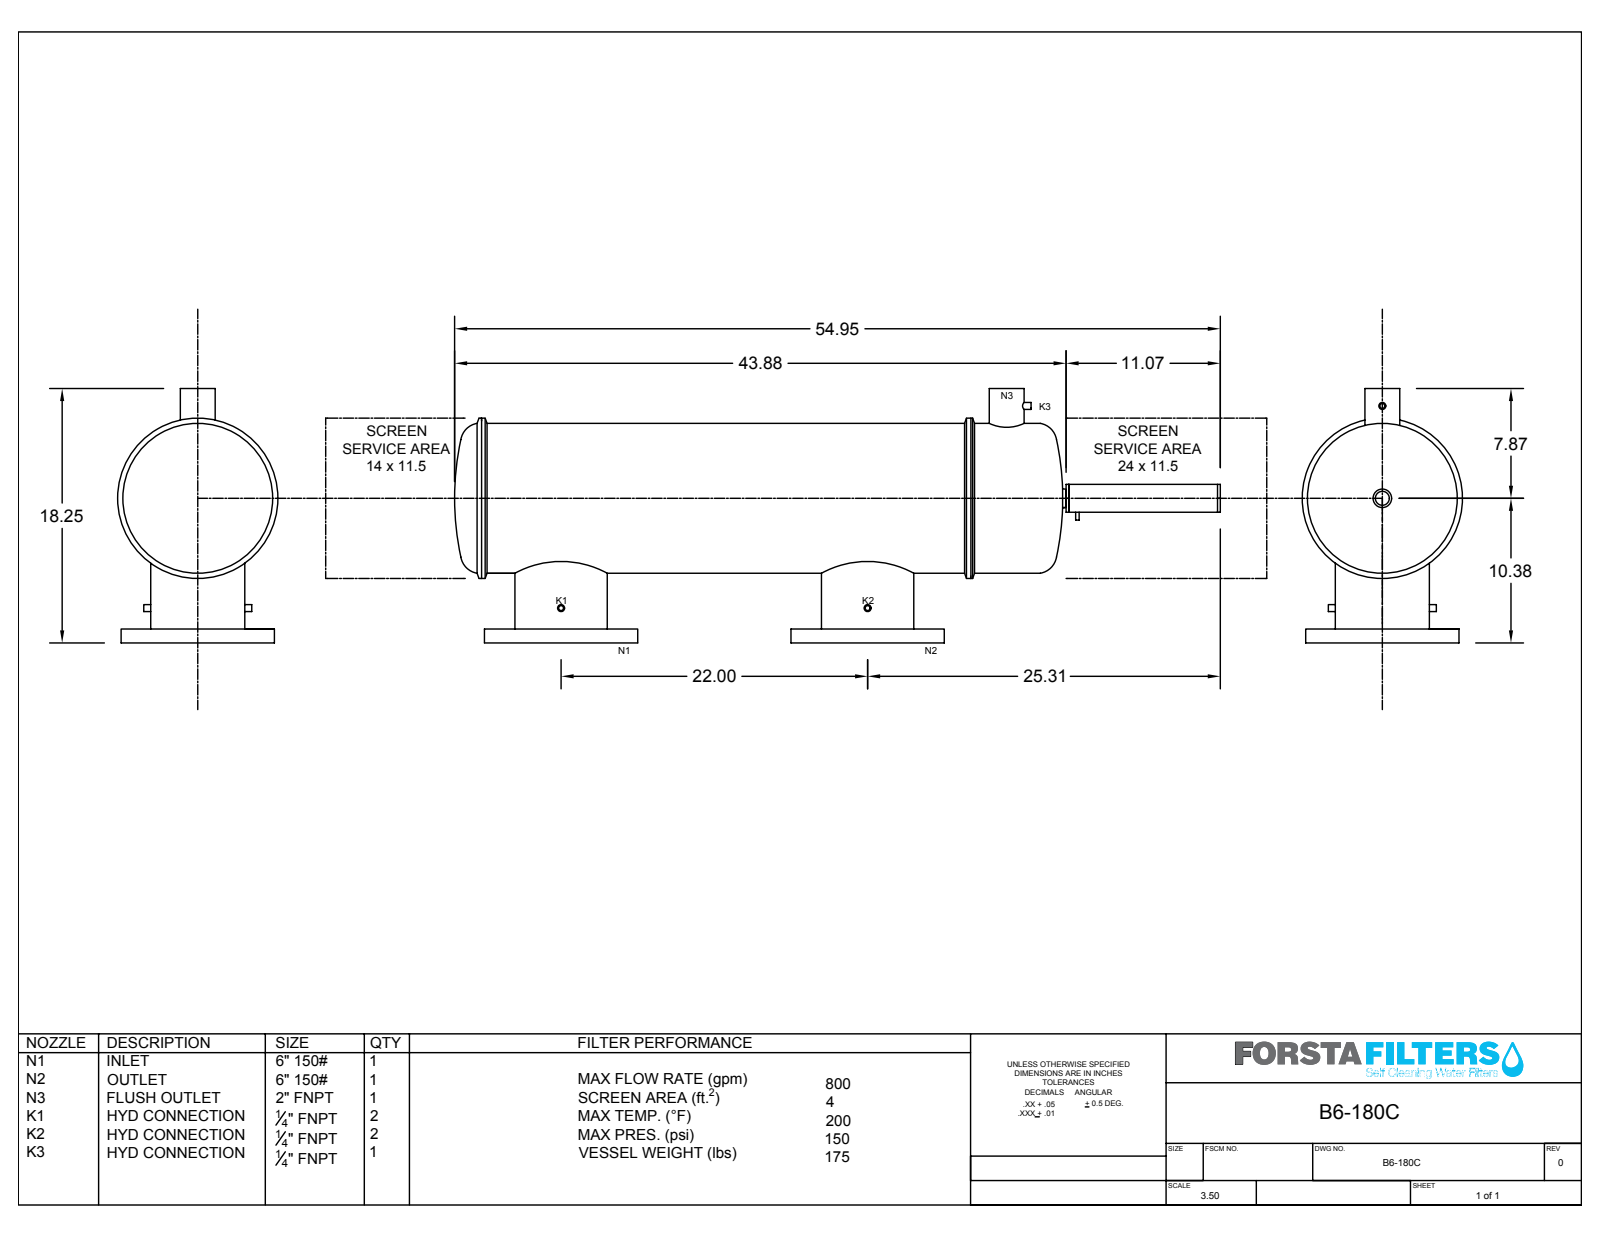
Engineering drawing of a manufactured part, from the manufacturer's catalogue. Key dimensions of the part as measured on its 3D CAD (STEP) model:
Part name (STEP PRODUCT): B6-180C
STEP written by: SolidWorks 2017 (CONFIG_CONTROL_DESIGN)
Units: inches
Bodies: 6 solids, 178 faces (42 planar, 102 cylindrical, 34 other)
Overall size (bounding box): 62.722 × 18.25 × 11.5
Volume: 538.3 in³ · Surface area: 4 358 in²
Round holes (diameter × count): ⌀0.88 ×16, ⌀0.25 ×3, ⌀1 ×2, ⌀6 ×2, ⌀0.093 ×1, ⌀0.936 ×1, ⌀2 ×1, ⌀10.356 ×1
Round bosses / shafts (diameter × count): ⌀0.644 ×3, ⌀11 ×2, ⌀6.394 ×2, ⌀11.5 ×1, ⌀10.75 ×1, ⌀2.394 ×1, ⌀2 ×1, ⌀1.33 ×1
Partial cylindrical surfaces — rounded edges, fillets, slot ends (radius × count): R1 ×2
Main face-to-face distances: 1, 37.868, 0.25, 0.2, 14.042, 60.335, 22.467, 46.493, 8.625, 13.842
Hole centre spacings: 3.635, 4.75, 6.718, 24.4, 8.777, 8.777, 3.636, 4.75
